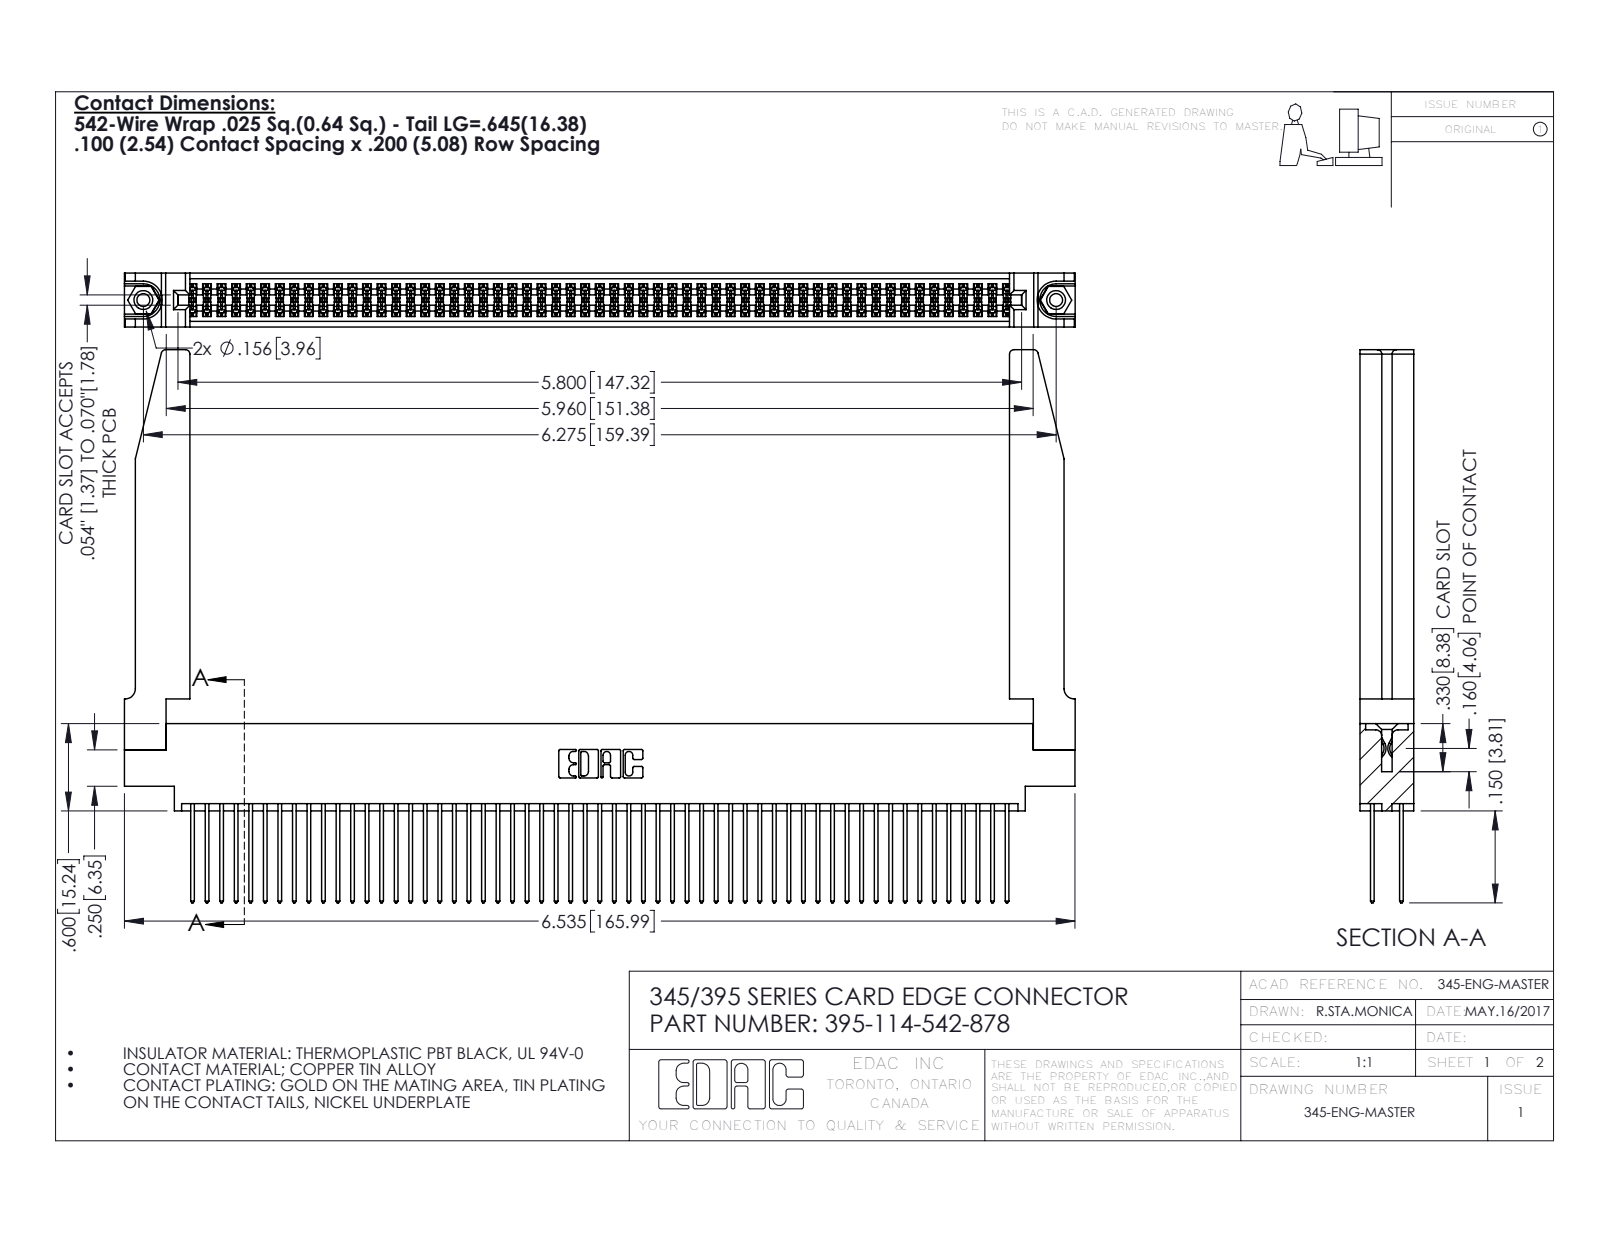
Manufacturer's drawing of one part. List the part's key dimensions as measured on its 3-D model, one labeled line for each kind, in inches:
Part name (STEP PRODUCT): 395-114-542-878; 345 Part_0.170 Offset - 0.156 Dia-TH; 345-250-001_345-250-001-102; 345-220-078_345-220-078 (+1 more)
STEP written by: SolidWorks 2016 (CONFIG_CONTROL_DESIGN)
Units: inches
Bodies: 119 solids, 6064 faces (3988 planar, 2024 cylindrical, 52 other)
Overall size (bounding box): 6.536 × 3.802 × 0.37
Volume: 1.492 in³ · Surface area: 53.35 in²
Round holes (diameter × count): ⌀0.089 ×2, ⌀0.125 ×2, ⌀0.156 ×2, ⌀0.064 ×1
Round bosses / shafts (diameter × count): ⌀0.155 ×2
Partial cylindrical surfaces — rounded edges, fillets, slot ends (radius × count): R0.006 ×171, R0.01 ×114, R0.01 ×22, R0.03 ×8, R0.007 ×6, R0.031 ×6, R0.026 ×3, R0.014 ×2
Main face-to-face distances: 0.072, 0.298, 0.37, 0.098, 0.272, 0.025, 0.2, 0.225, 0.175, 0.148
Hole centre spacings: 0.27, 6.039, 6.275
